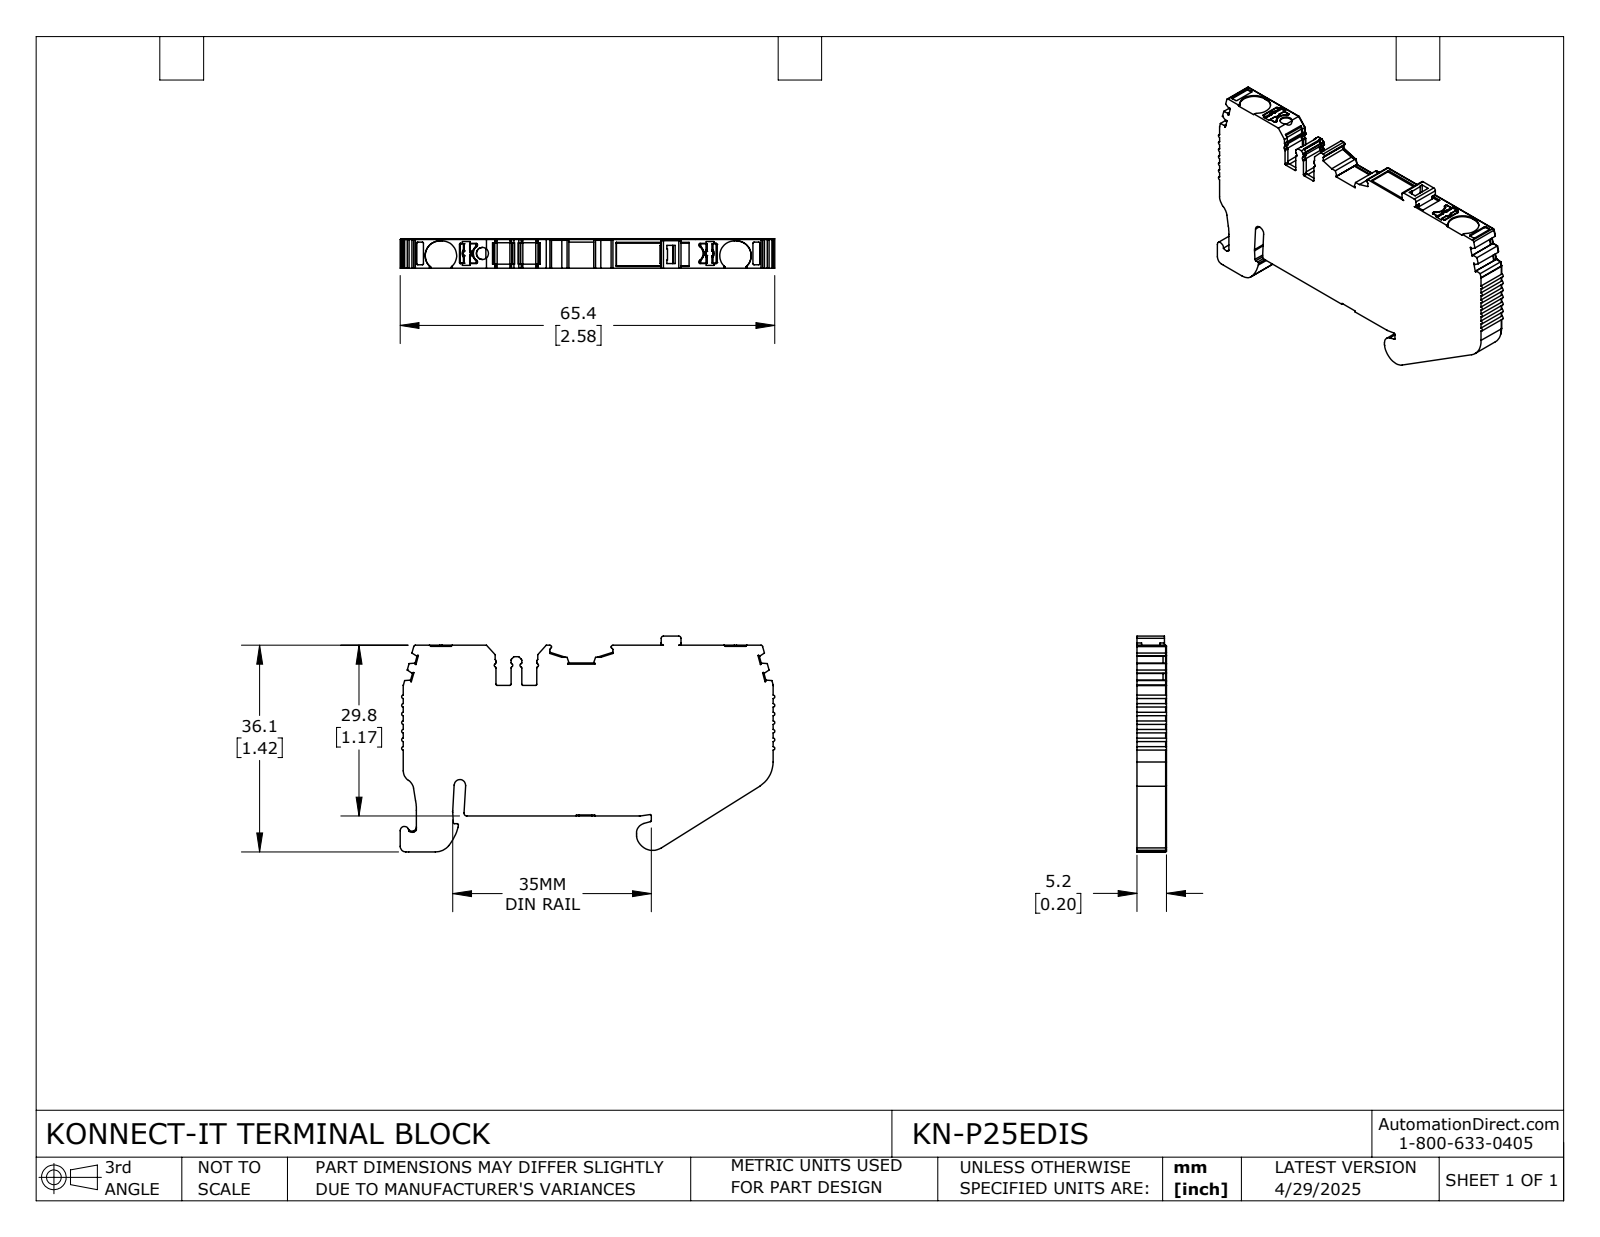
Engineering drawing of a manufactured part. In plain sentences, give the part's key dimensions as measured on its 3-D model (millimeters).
The part is named "KN-P25EDIS". Its 3-D file was written by "SolidWorks 2024 (CONFIG_CONTROL_DESIGN)". It is 1 solid with 618 faces: 346 planar, 237 cylindrical and 35 other. Overall it measures 65.42 by 37.67 by 5.15 millimeters. Its volume is 9 594 cubic millimeters and its surface area 5 183 square millimeters. Round holes: 1 of diameter 2.1. Partial cylindrical surfaces (rounded edges, fillets, slot ends): 54 of radius 0.2, 39 of radius 0.3, 18 of radius 0.5, 17 of radius 0.1, 13 of radius 0.4, 8 of radius 0.15, 4 of radius 1, 4 of radius 2.55. The main face-to-face distances are 5.15, 29.61, 29.81, 64.58, 4.5, 5, 2, 6.26, 35.87, 36.07.
